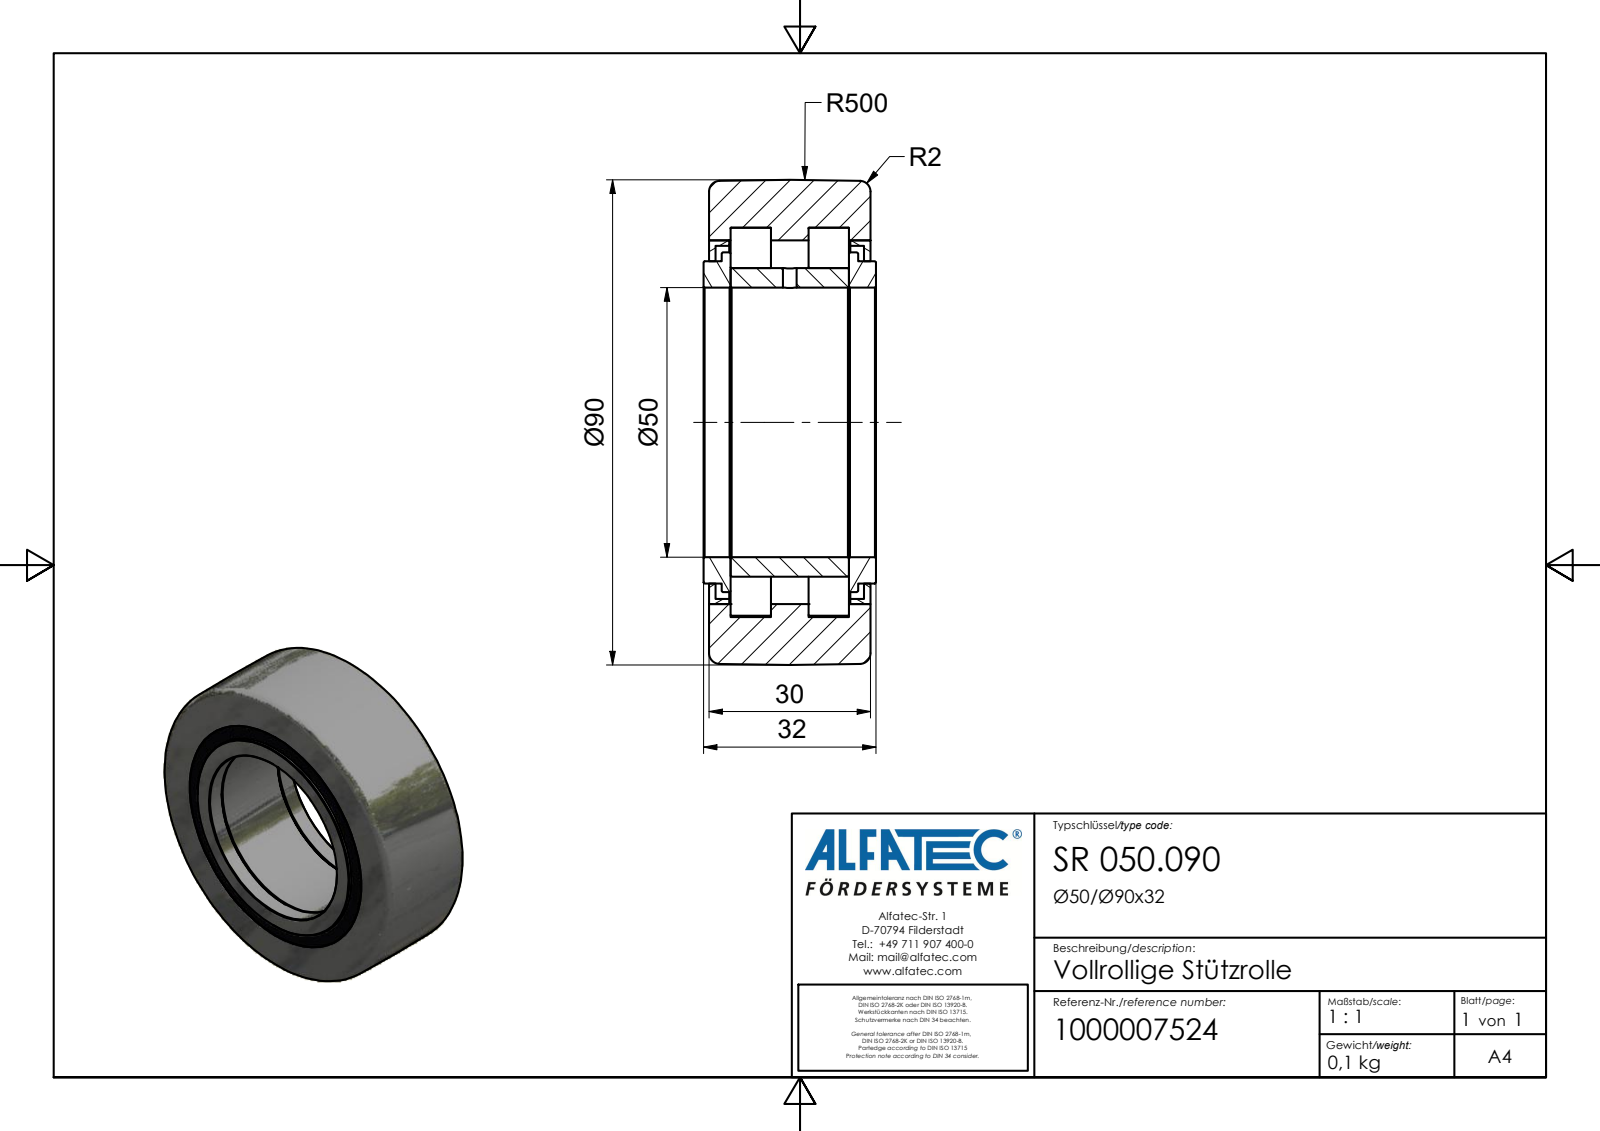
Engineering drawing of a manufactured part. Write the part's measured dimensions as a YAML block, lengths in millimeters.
part_name: "SR 050.090_Kontur"
step_written_by: "Autodesk Inventor 2020 (AUTOMOTIVE_DESIGN)"
units: millimeters
bodies: {solids: 1, faces: 222, planar: 72, cylindrical: 77, other: 73}
overall_size: [90, 90, 32]
volume: 109673
surface_area: 43881
round_holes:
  - {diameter: 2.5, count: 1}
  - {diameter: 50, count: 1}
  - {diameter: 65.58, count: 1}
  - {diameter: 67.5, count: 1}
  - {diameter: 72.24, count: 1}
round_bosses_or_shafts:
  - {diameter: 7.5, count: 14}
  - {diameter: 63.07, count: 1}
  - {diameter: 59.8, count: 1}
  - {diameter: 57.24, count: 1}
face_to_face_distances: [30, 4, 26, 11.5, 18.5, 7.5, 14.5, 1, 5, 12.5]
